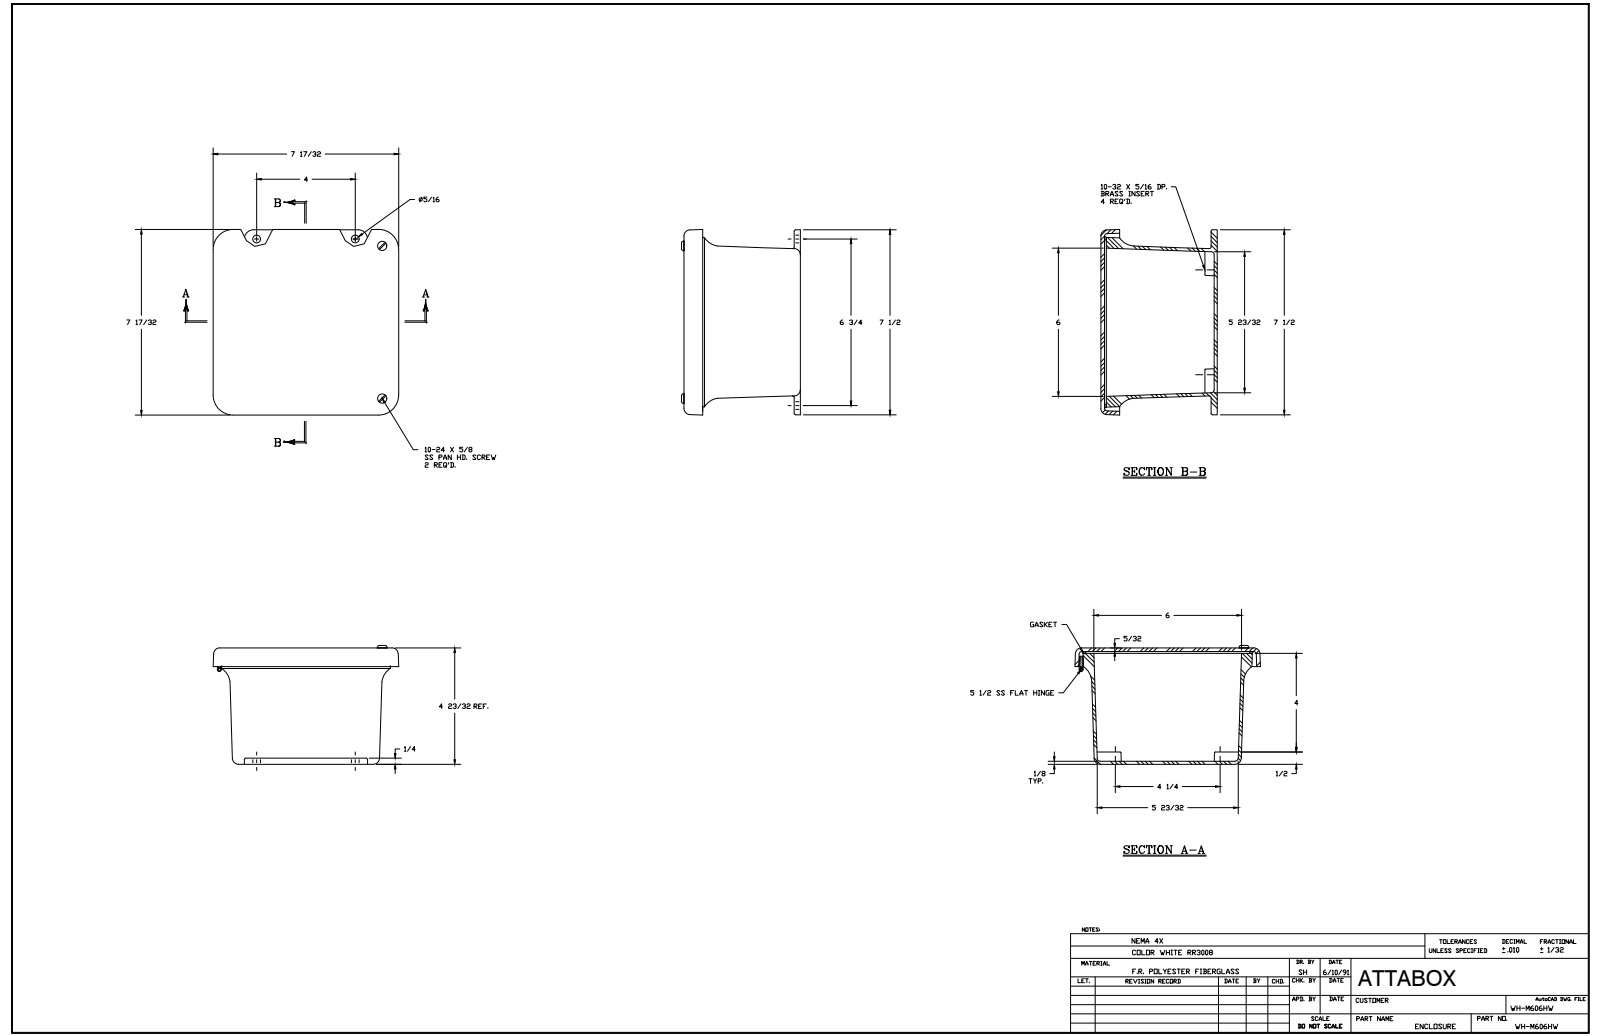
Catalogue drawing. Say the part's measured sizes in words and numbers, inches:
The part is named "WH-M606HW". Its 3-D file was written by "SolidWorks 2018 (AUTOMOTIVE_DESIGN)". It is 19 solids with 649 faces: 200 planar, 247 cylindrical and 202 other. Overall it measures 7.553 by 7.525 by 4.969 inches. Its volume is 37.8 cubic inches and its surface area 502.7 square inches. Round holes: 5 of diameter 0.131, 5 of diameter 0.14, 5 of diameter 0.152, 4 of diameter 0.156, 4 of diameter 0.218, 2 of diameter 0.145, 1 of diameter 0.085, 1 of diameter 0.085. Round bosses or shafts: 6 of diameter 0.27, 5 of diameter 0.25, 4 of diameter 0.125, 2 of diameter 0.19, 2 of diameter 0.156, 1 of diameter 0.155, 1 of diameter 0.155, 1 of diameter 0.125. Partial cylindrical surfaces (rounded edges, fillets, slot ends): 20 of radius 0.031, 12 of radius 0.25, 8 of radius 0.125, 4 of radius 0.063, 4 of radius 0.2, 4 of radius 0.375, 4 of radius 0.75, 2 of radius 0.063. The main face-to-face distances are 0.147, 4.691, 4.838, 0.125, 4.566, 4.713, 0.152, 4.5, 0.213, 4.625. The hole center spacings are 5.308, 1.37, 2.5, 4.25, 6.187, 7.38, 0.5, 2.
